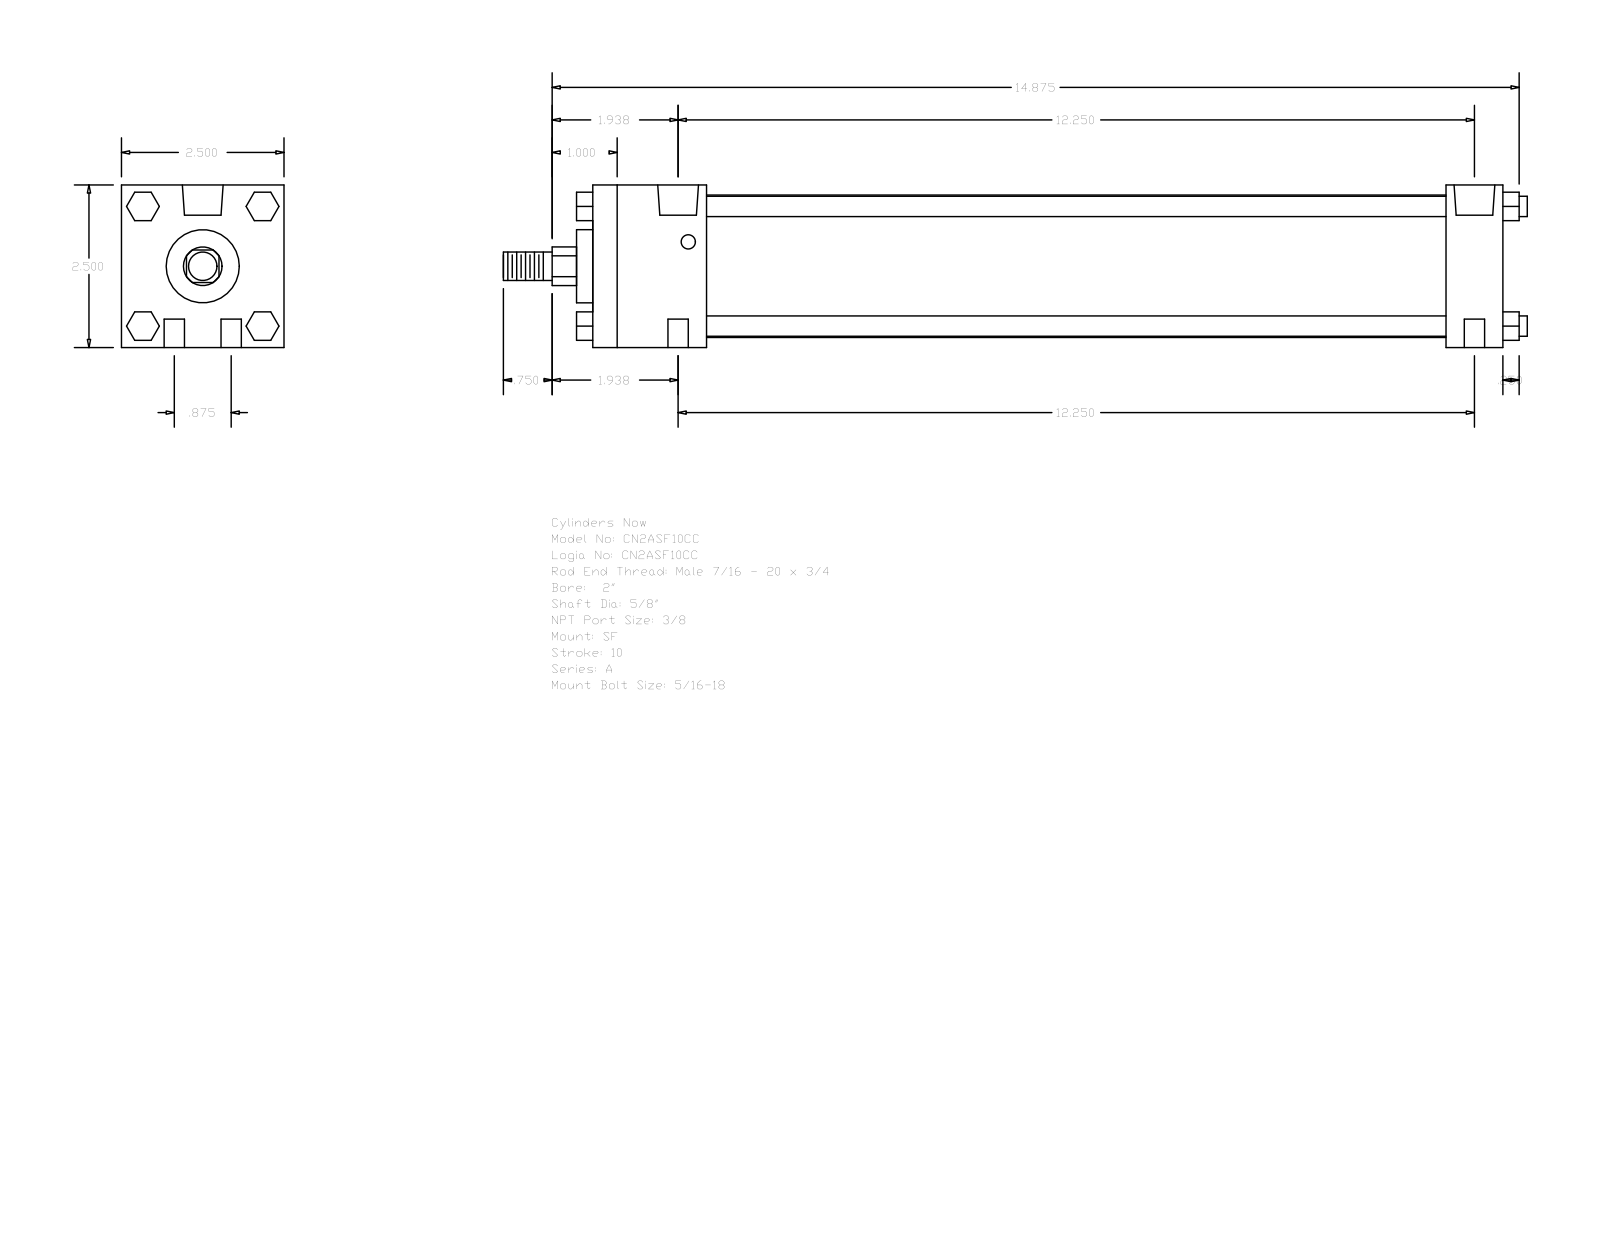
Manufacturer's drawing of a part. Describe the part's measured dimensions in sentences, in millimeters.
The part is named "A_SF__0200_0.625". Its 3-D file was written by "GSSL Pune (CONFIG_CONTROL_DESIGN)". It is 0 solids with 124 faces: 94 planar, 30 cylindrical and 0 other. Overall it measures 400.05 by 63.5 by 63.5 millimeters. Round holes: 4 of diameter 7.94, 2 of diameter 5.56, 2 of diameter 15.93. Round bosses or shafts: 4 of diameter 7.94, 1 of diameter 55.63, 1 of diameter 28.57, 1 of diameter 15.88, 1 of diameter 11.11. Partial cylindrical surfaces (rounded edges, fillets, slot ends): 1 of radius 7.54. The main face-to-face distances are 63.5, 355.6, 333.37, 22.23, 44.45, 288.92, 311.15, 50.8, 6.35, 339.72. The hole center spacings are 11.11, 311.35, 311.15, 22.22, 311.94, 303.2.
